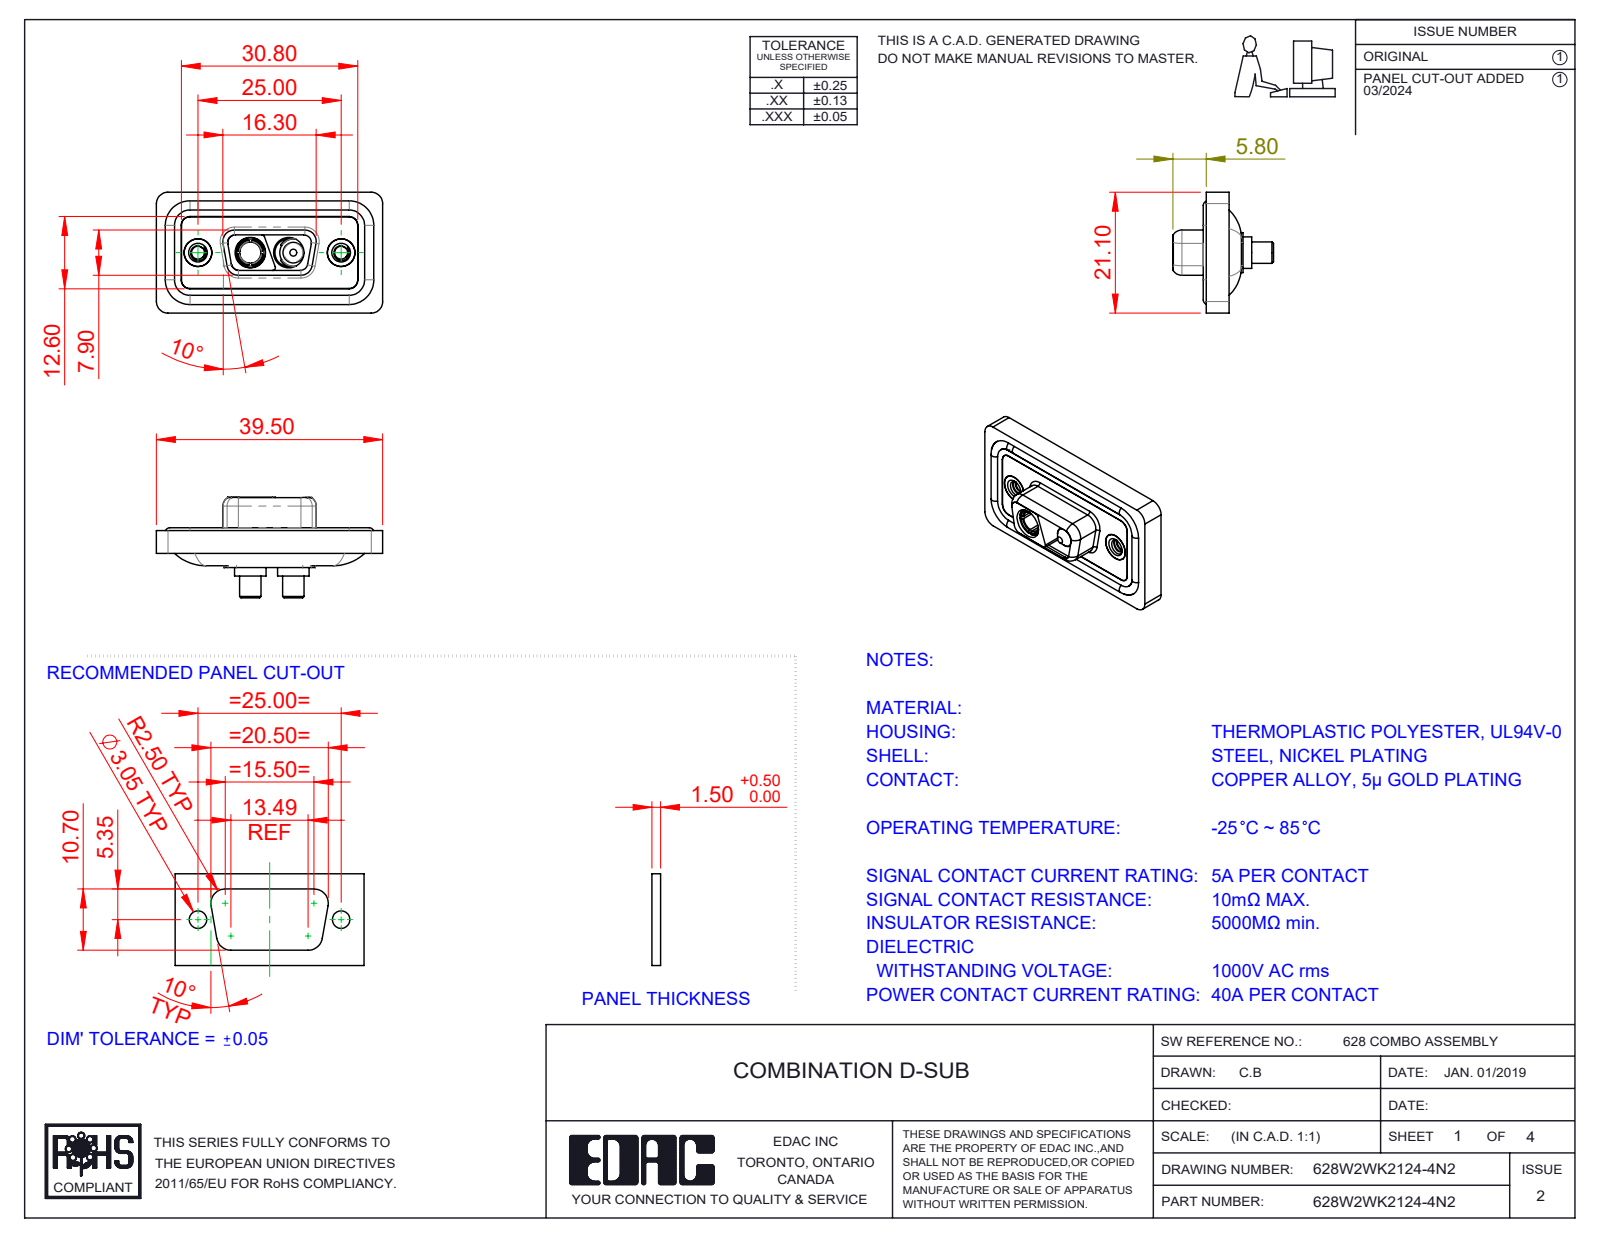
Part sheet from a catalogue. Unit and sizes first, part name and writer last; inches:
Units: inches
Overall size (bounding box): 1.555 × 0.831 × 0.691
Round holes (diameter × count): ⌀0.191 ×4, ⌀0.089 ×2, ⌀0.157 ×2, ⌀0.159 ×2, ⌀0.197 ×2, ⌀0.209 ×2, ⌀0.146 ×1
Round bosses / shafts (diameter × count): ⌀0.063 ×4, ⌀0.217 ×2, ⌀0.205 ×2, ⌀0.195 ×2, ⌀0.189 ×2, ⌀0.187 ×2, ⌀0.148 ×2, ⌀0.195 ×1
Partial cylindrical surfaces — rounded edges, fillets, slot ends (radius × count): R0.059 ×22, R0.079 ×18, R0.053 ×8, R0.063 ×8, R0.02 ×6, R0.01 ×4, R0.024 ×4, R0.026 ×4
Main face-to-face distances: 0.016, 0.043, 0.114, 0.063, 0.02, 0.071, 0.222, 0.211, 0.122, 0.059
Hole centre spacings: 0.36, 0.624, 0.265, 0.984
Volume: 0.283 in³ · Surface area: 11.42 in²
Bodies: 11 solids, 500 faces (144 planar, 231 cylindrical, 125 other)
Part name (STEP PRODUCT): Power Socket_40A S; 628Combo Shell Front_09 Contacts; 628Combo Threaded Rivet_2; 628Combo Shell Rear_09 Contacts (+4 more)
STEP written by: SolidWorks 2023 (CONFIG_CONTROL_DESIGN)
